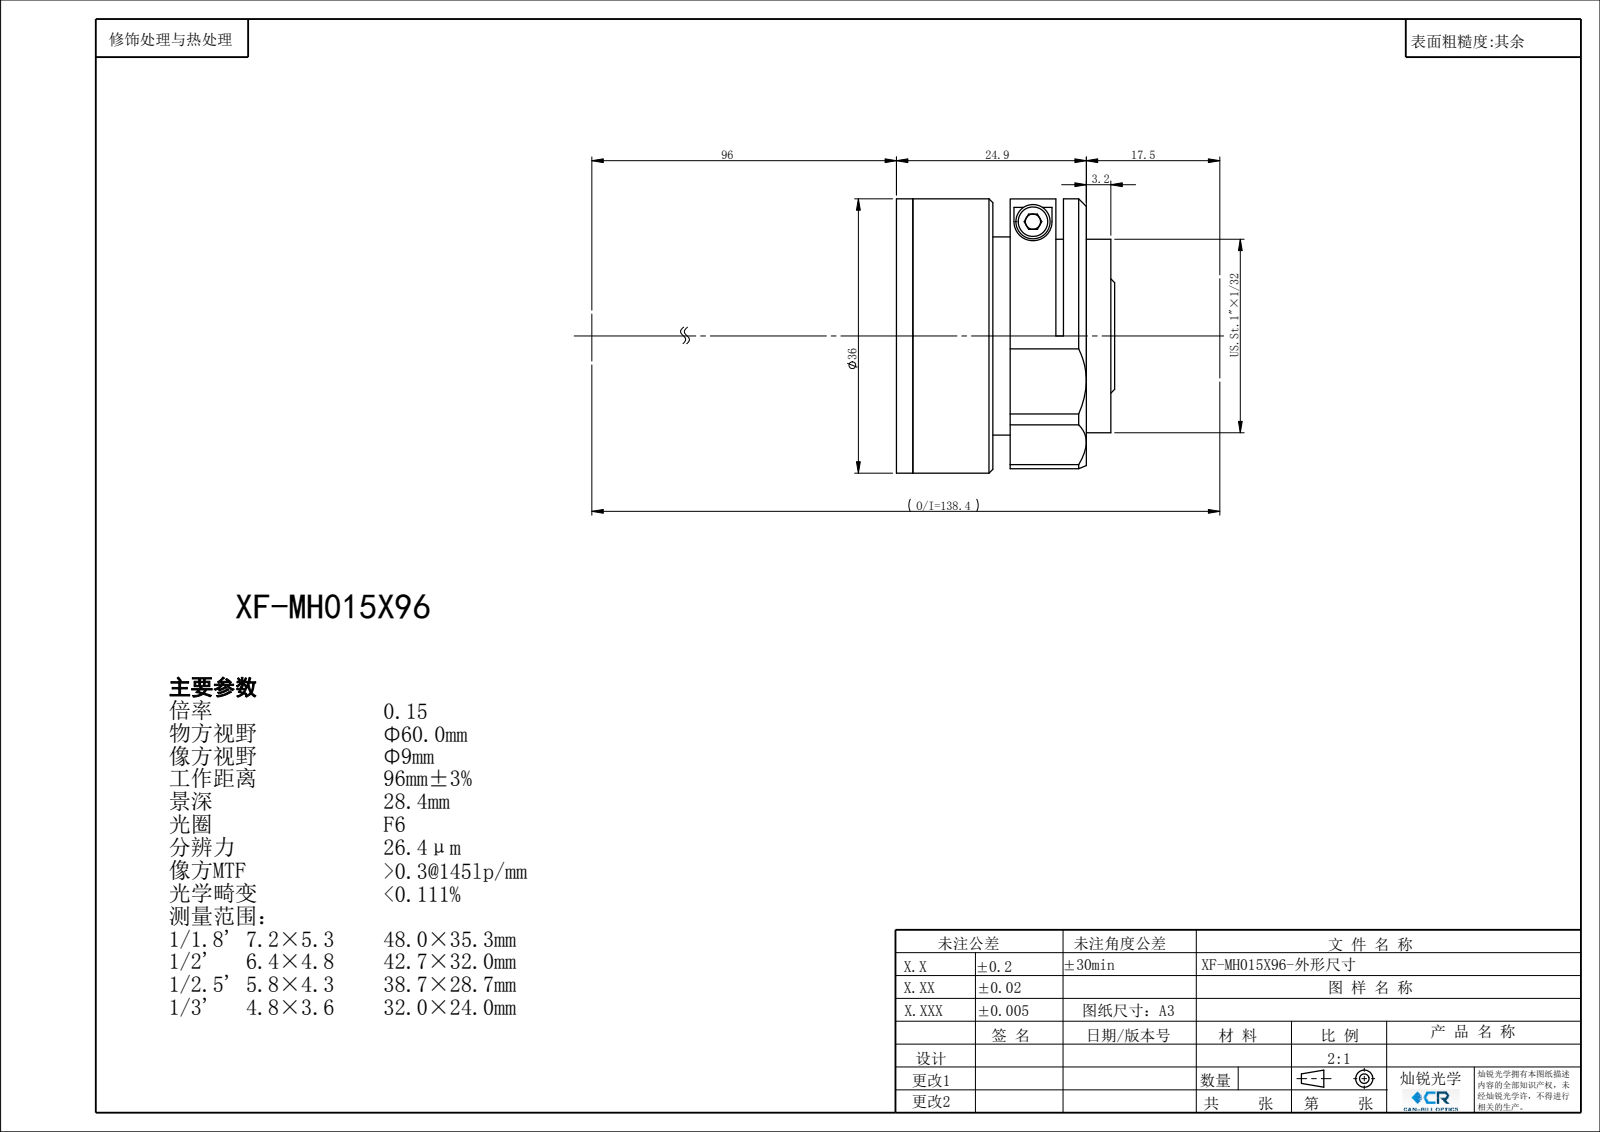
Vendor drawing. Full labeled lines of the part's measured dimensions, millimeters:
Part name (STEP PRODUCT): XF-MH015X96
STEP written by: SolidWorks 2018 (CONFIG_CONTROL_DESIGN)
Units: millimetres
Bodies: 2 solids, 158 faces (59 planar, 80 cylindrical, 19 other)
Overall size (bounding box): 36 × 36 × 28.65
Volume: 18 704 mm³ · Surface area: 12 466 mm²
Round holes (diameter × count): ⌀2.05 ×1, ⌀3 ×1, ⌀7 ×1, ⌀7.4 ×1, ⌀8.4 ×1, ⌀10 ×1, ⌀12 ×1, ⌀14 ×1, ⌀16 ×1, ⌀18 ×1, ⌀21 ×1, ⌀22 ×1
Round bosses / shafts (diameter × count): ⌀36 ×1, ⌀30 ×1, ⌀28 ×1, ⌀25.4 ×1, ⌀23.4 ×1, ⌀20 ×1, ⌀9.14 ×1, ⌀4.5 ×1
Partial cylindrical surfaces — rounded edges, fillets, slot ends (radius × count): R25 ×5, R2.5 ×1
Main face-to-face distances: 2, 14.93, 2.28, 10, 12.65, 10.65, 1.5, 1, 6, 4.28
